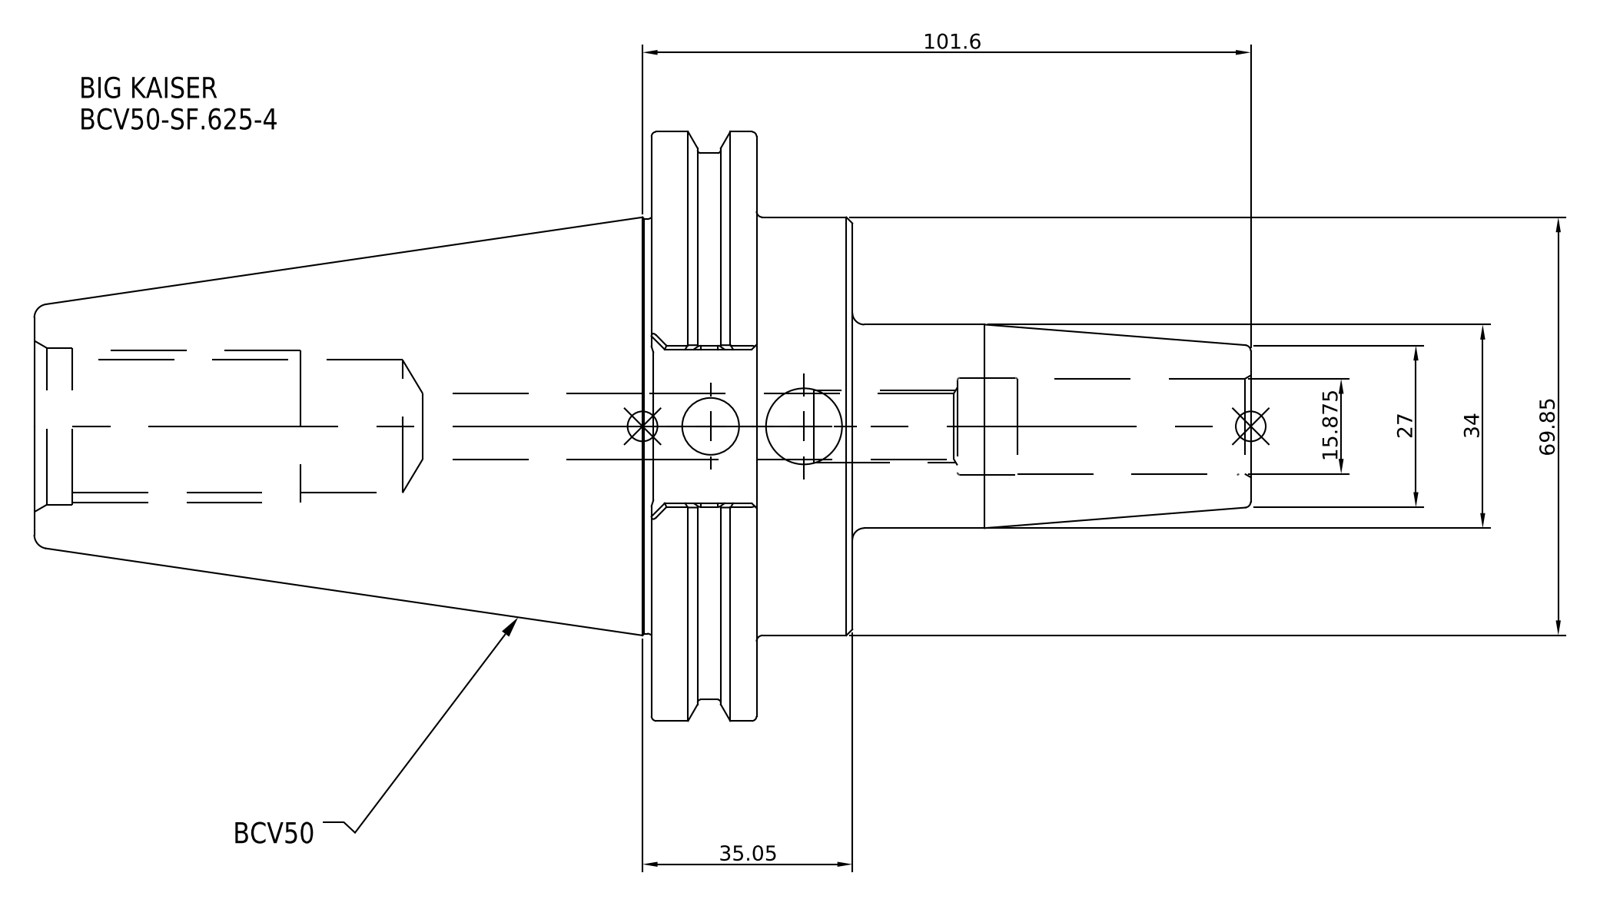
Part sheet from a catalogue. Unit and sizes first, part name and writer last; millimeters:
Units: millimetres
Overall size (bounding box): 203.2 × 98.43 × 98.43
Round holes (diameter × count): ⌀15.88 ×1
Round bosses / shafts (diameter × count): ⌀98.43 ×1, ⌀91.29 ×1, ⌀69.85 ×1, ⌀34 ×1
Main face-to-face distances: 17.55, 16, 33.55, 136.65, 120.65, 103.1, 66.55, 82.55, 100.1, 203.2
Volume: 487 633 mm³ · Surface area: 49 226 mm²
Bodies: 1 solid, 30 faces (8 planar, 14 cylindrical, 8 other)
Part name (STEP PRODUCT): BCV50-SF_625-4
STEP written by: SolidWorks 2021 (CONFIG_CONTROL_DESIGN)
